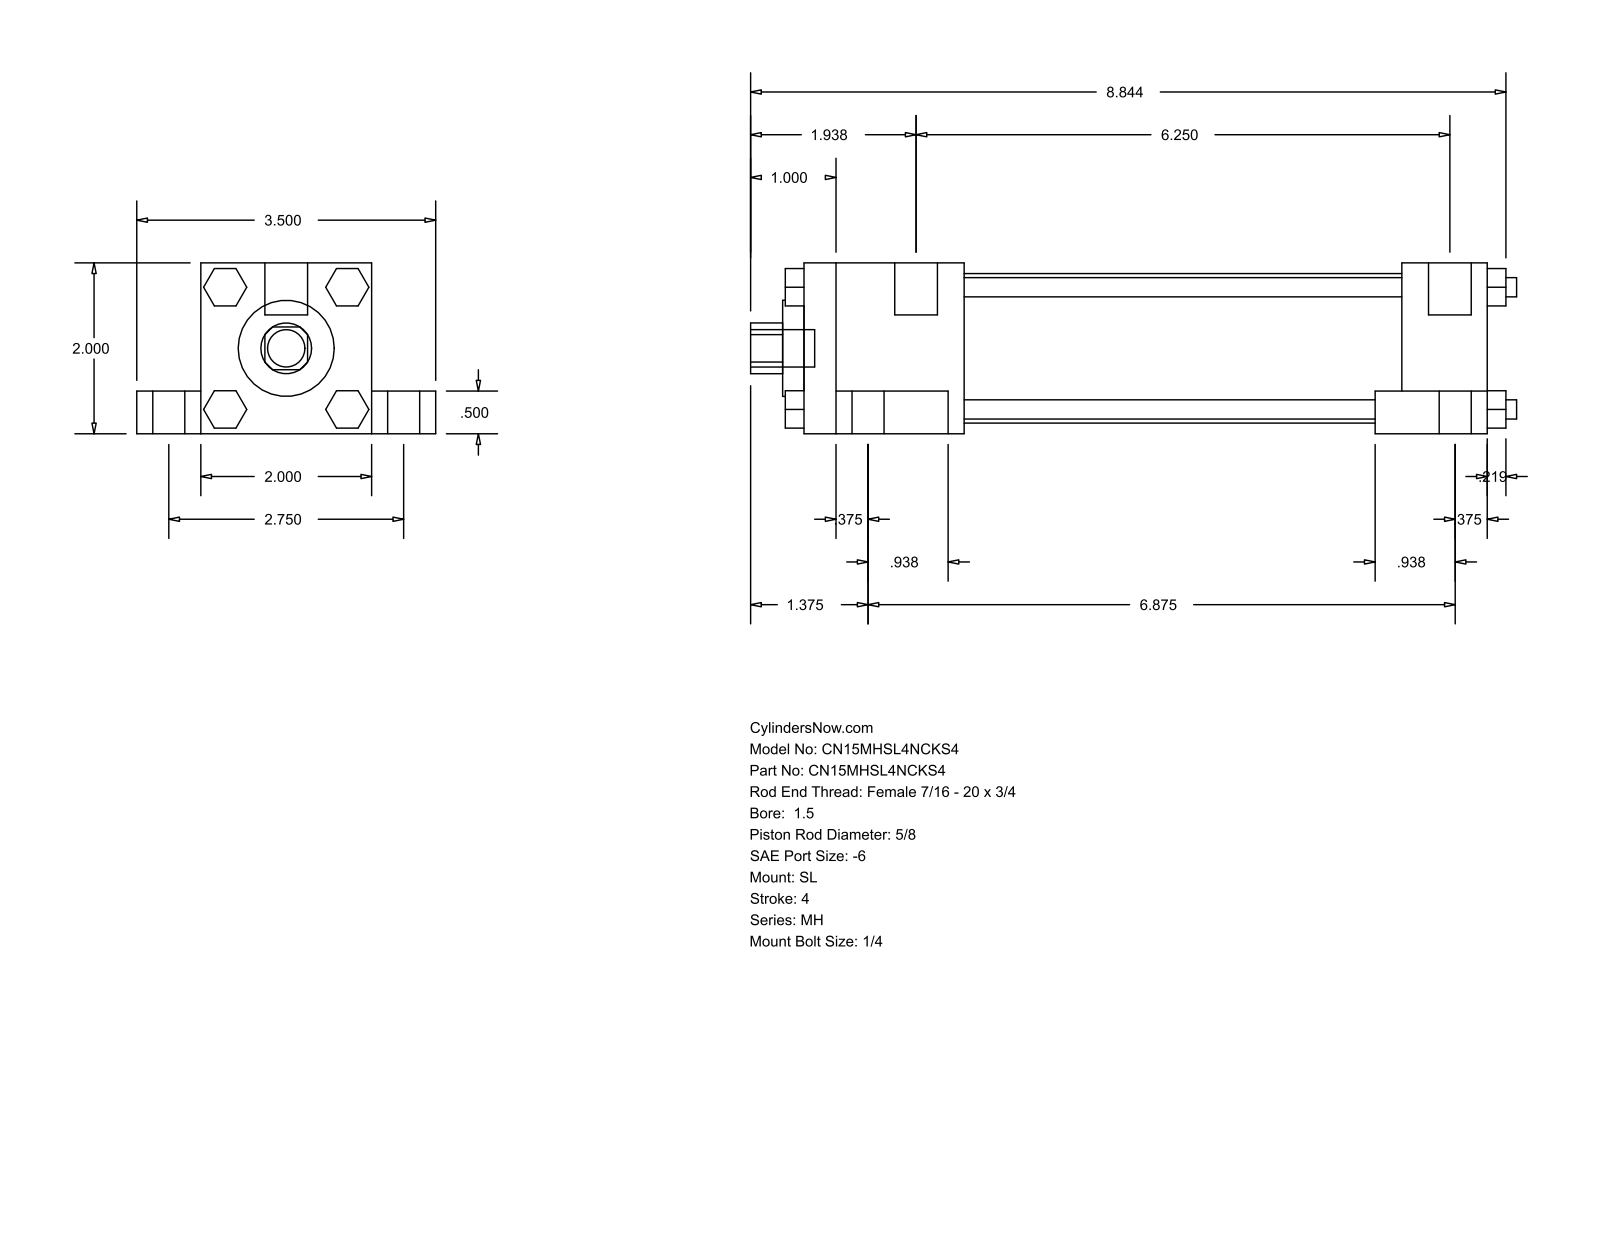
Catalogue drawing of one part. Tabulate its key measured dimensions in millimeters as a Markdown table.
| quantity | value |
| --- | --- |
| part name | MH_SL__0150_0.625 |
| STEP written by | GSSL Pune (CONFIG_CONTROL_DESIGN) |
| units | millimeters |
| bodies | 0 solids, 148 faces (112 planar, 36 cylindrical, 0 other) |
| overall size | 227.81 × 88.9 × 50.8 |
| round holes (diameter × count) | 15.88 × 1, 28.57 × 1, 44.45 × 1 |
| round bosses / shafts (diameter × count) | 15.88 × 4, 9.53 × 4, 5.71 × 4, 5.56 × 4, 12.7 × 2, 11.11 × 1 |
| partial cylindrical surfaces (radius × count) | 7.54 × 1 |
| main face-to-face distances | 50.8, 38.1, 19.05, 12.7, 69.85, 203.19, 9.52, 177.8, 25.39, 47.62 |
